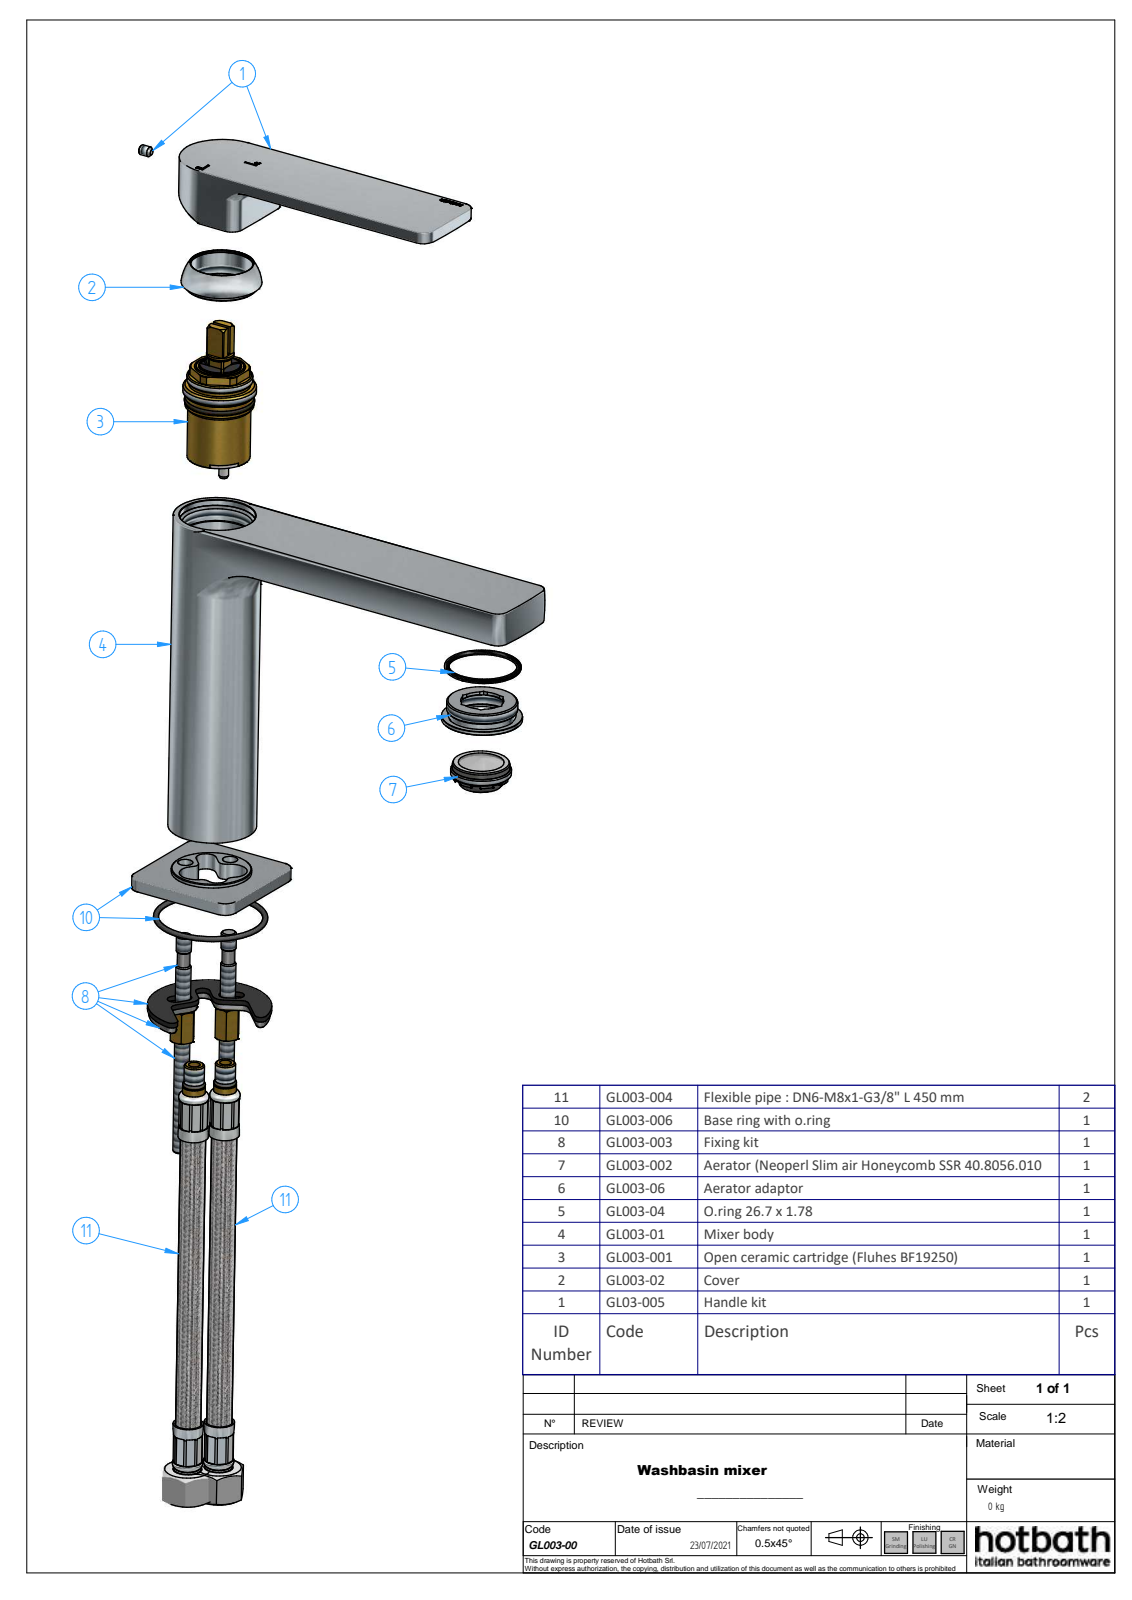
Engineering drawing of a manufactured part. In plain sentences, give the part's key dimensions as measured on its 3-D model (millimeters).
The part is named "GL003-00; GL003-02; GL003-05; GL003-09 (+8 more)". Its 3-D file was written by "ST-DEVELOPER v16.7 (AUTOMOTIVE_DESIGN)". It is 11 solids with 886 faces: 223 planar, 216 cylindrical and 447 other. Overall it measures 169.5 by 162.8 by 48 millimeters. Its volume is 110 419 cubic millimeters and its surface area 79 789 square millimeters. Round holes: 3 of diameter 4, 2 of diameter 4.92, 2 of diameter 5.5, 2 of diameter 6, 2 of diameter 6.92, 2 of diameter 9, 2 of diameter 12, 1 of diameter 3.24, 1 of diameter 4.2, 1 of diameter 15.8, 1 of diameter 16, 1 of diameter 18. Round bosses or shafts: 1 of diameter 35, 1 of diameter 32, 1 of diameter 31.7, 1 of diameter 28.5, 1 of diameter 28, 1 of diameter 26.8, 1 of diameter 24, 1 of diameter 22.7. Partial cylindrical surfaces (rounded edges, fillets, slot ends): 32 of radius 0.1, 14 of radius 2.5, 13 of radius 0.5, 12 of radius 1, 10 of radius 2, 10 of radius 5, 8 of radius 0.2, 6 of radius 3. The main face-to-face distances are 1.5, 5, 122.9, 3.5, 127.9, 6.5, 124.4, 126.4, 129.4, 121.4. The hole center spacings are 1.57, 3.18, 6.21, 7.16, 8.04, 9.37, 10.4, 11.01.
